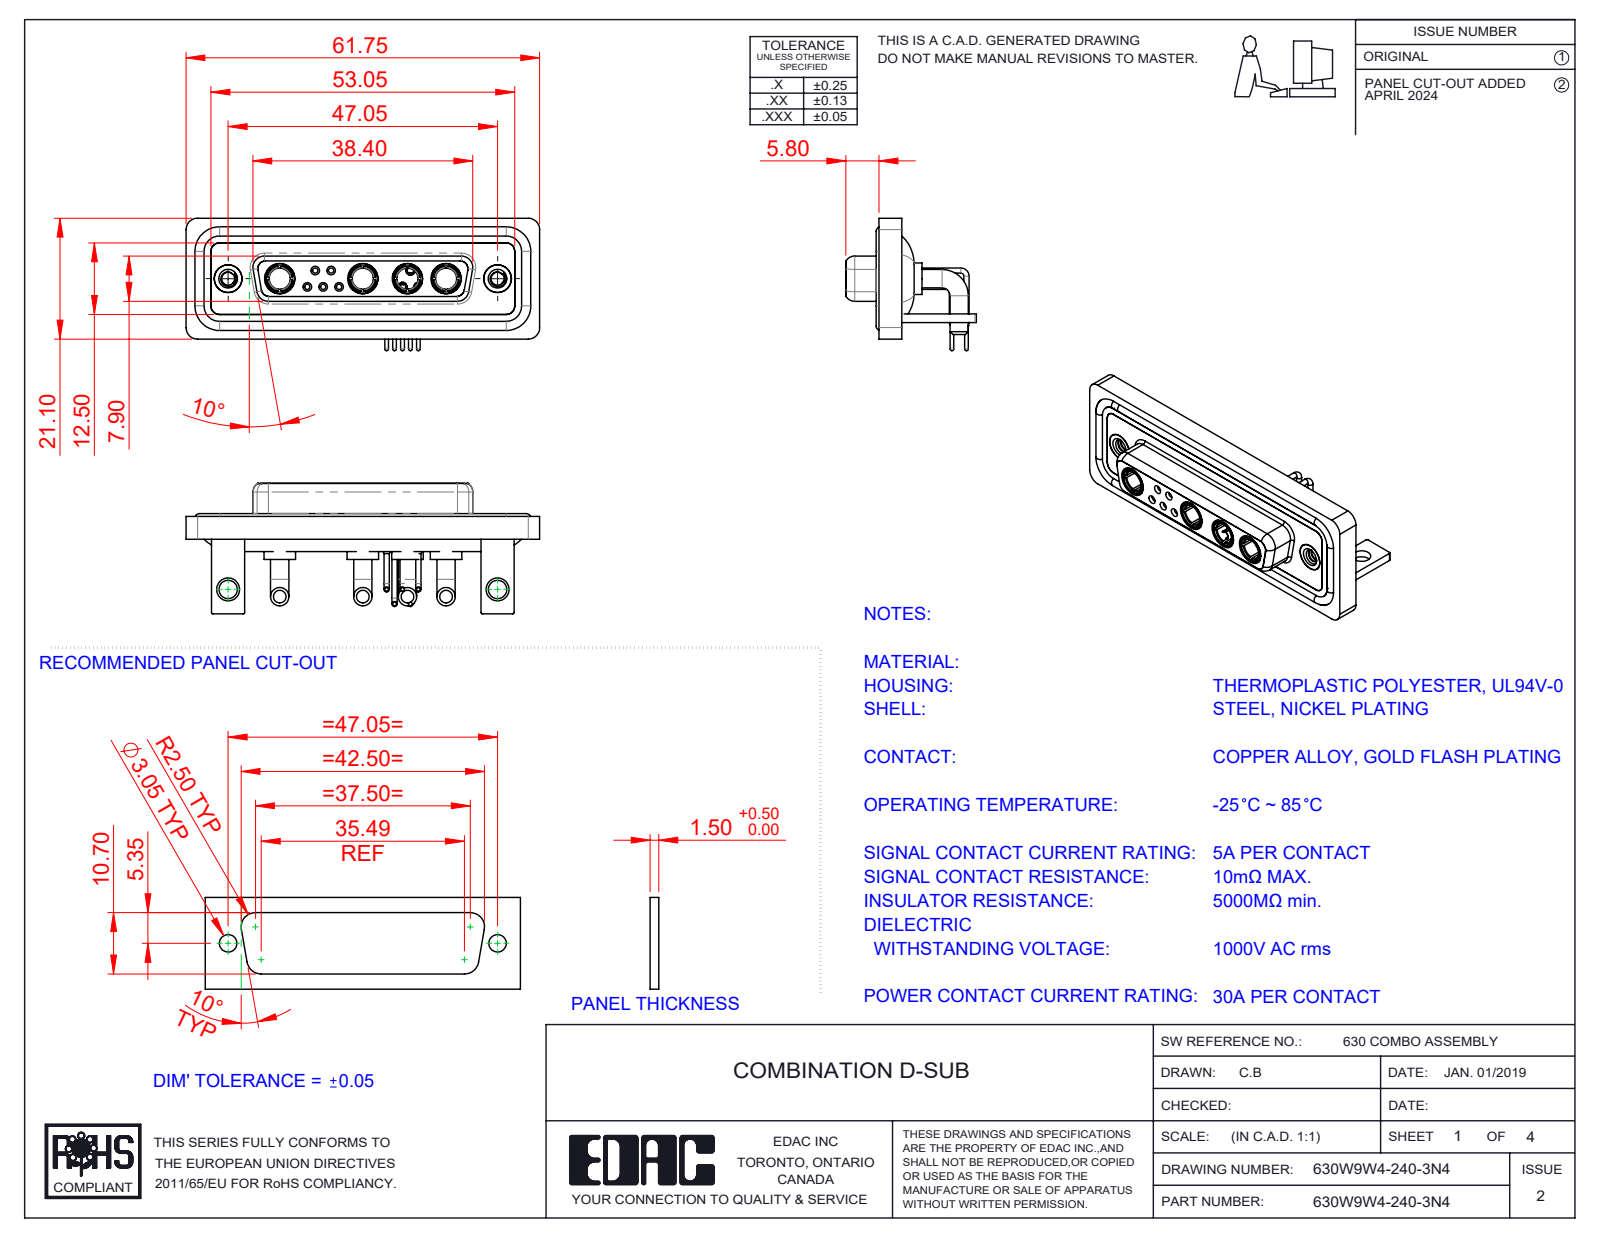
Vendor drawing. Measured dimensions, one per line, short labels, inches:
name: 630Combo Contact Row 2_50 Contacts; 630Combo Stabilizer Bracket_50 Contacts; 630Combo Waterproof Housing_25 Contacts; 630Combo Contact Row 1_50 Contacts (+6 more)
written by: SolidWorks 2023 (CONFIG_CONTROL_DESIGN)
unit: in
bodies: 22 solids, 1011 faces (316 planar, 427 cylindrical, 268 other)
size: 2.431 × 0.91 × 0.898
volume: 0.545 in³; area: 23.03 in²
holes: 6× ⌀0.191, 5× ⌀0.035, 5× ⌀0.043, 5× ⌀0.059, 5× ⌀0.079, 4× ⌀0.146, 4× ⌀0.209, 3× ⌀0.063, 2× ⌀0.067, 2× ⌀0.089, 2× ⌀0.126, 2× ⌀0.157
bosses: 10× ⌀0.035, 9× ⌀0.063, 8× ⌀0.126, 5× ⌀0.079, 5× ⌀0.059, 5× ⌀0.026, 4× ⌀0.217, 4× ⌀0.205
rounds: 19× R0.079, 18× R0.059, 16× R0.01, 8× R0.053, 8× R0.063, 5× R0.02, 4× R0.024, 4× R0.026
face distances: 0.016, 0.071, 0.114, 0.146, 0.059, 0.161, 0.043, 0.055, 0.063, 0.098
hole spacings: 0.124, 0.109, 0.198, 0.545, 0.436, 0.504, 0.61, 0.218
